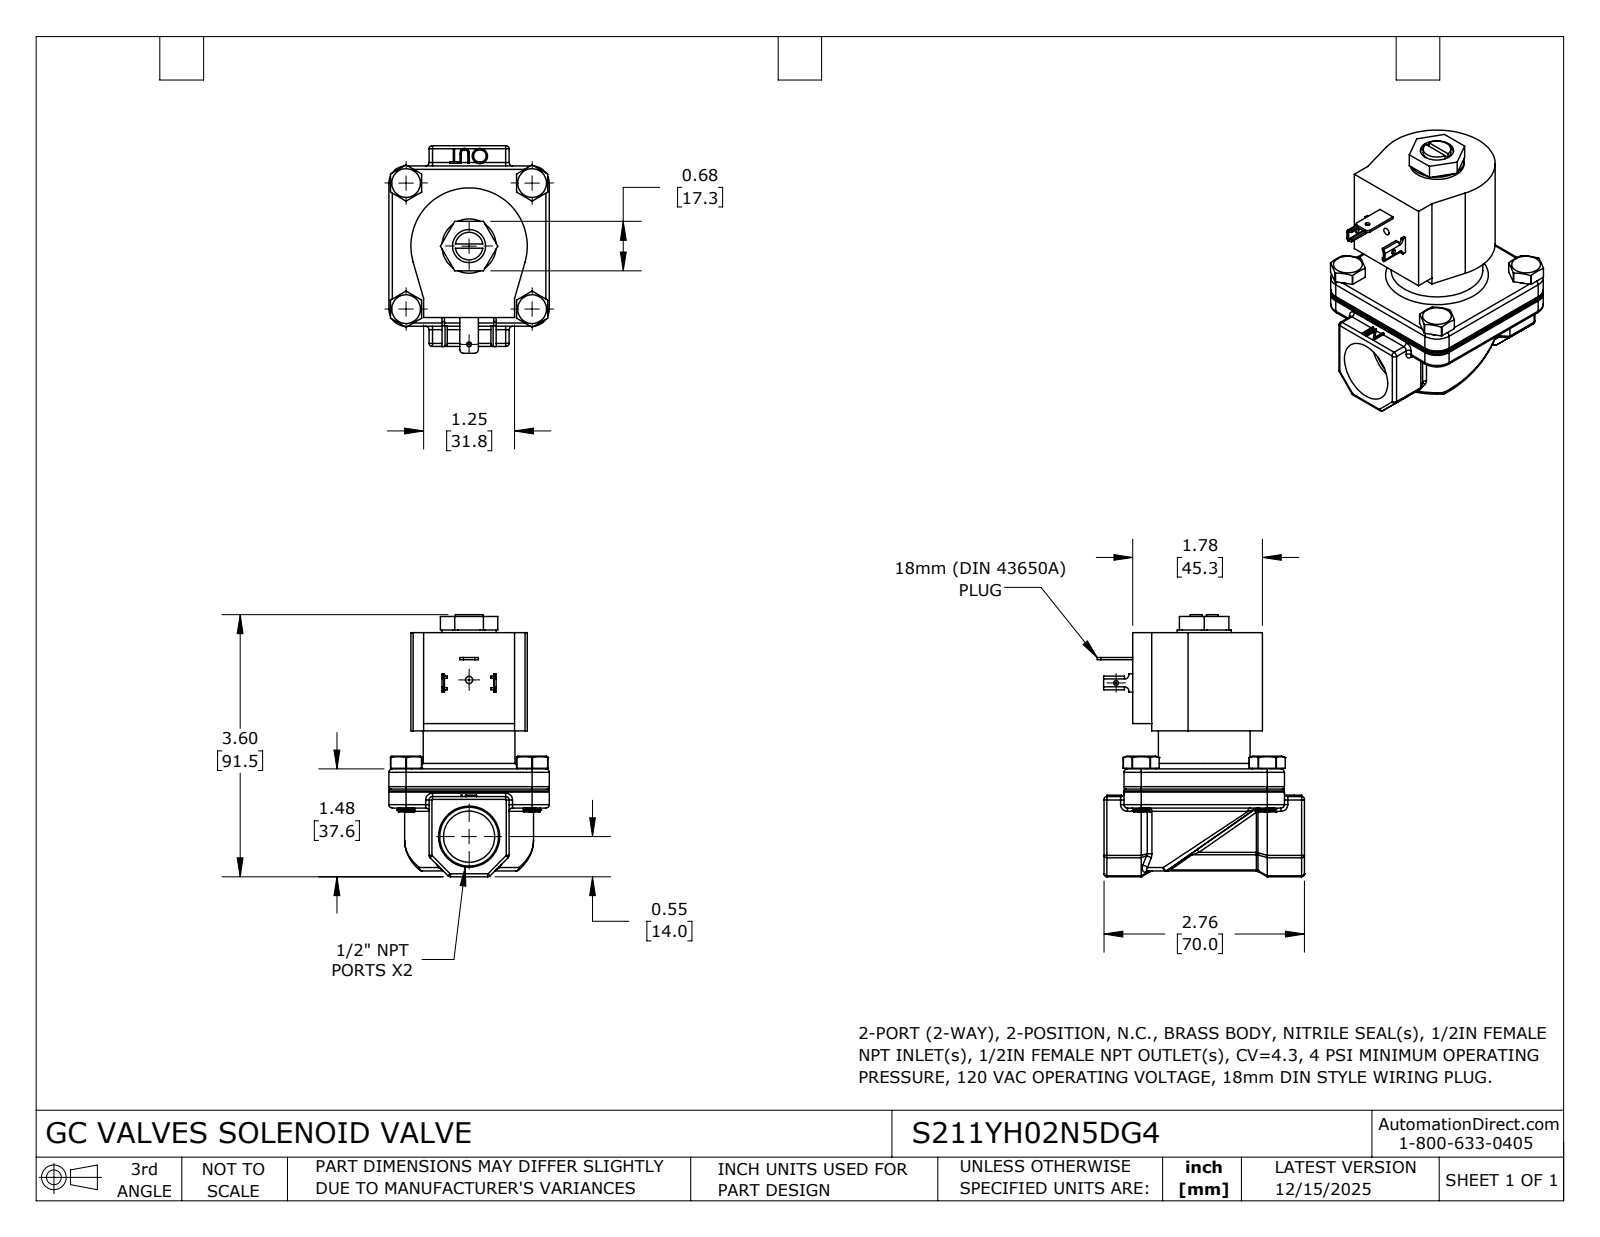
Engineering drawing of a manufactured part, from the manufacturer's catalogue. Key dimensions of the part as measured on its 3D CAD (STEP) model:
Part name (STEP PRODUCT): S211YH02N5DG4
STEP written by: SolidWorks 2024 (CONFIG_CONTROL_DESIGN)
Units: inches
Bodies: 1 solid, 521 faces (228 planar, 163 cylindrical, 130 other)
Overall size (bounding box): 3.601 × 2.851 × 2.205
Volume: 8.787 in³ · Surface area: 40.33 in²
Round holes (diameter × count): ⌀0.066 ×1, ⌀0.067 ×1, ⌀0.1 ×1, ⌀0.456 ×1, ⌀0.703 ×1
Round bosses / shafts (diameter × count): ⌀0.407 ×4, ⌀0.242 ×4, ⌀1.26 ×1, ⌀0.746 ×1, ⌀0.38 ×1
Partial cylindrical surfaces — rounded edges, fillets, slot ends (radius × count): R0.047 ×57, R0.04 ×12, R0.006 ×4, R0.031 ×4, R0.041 ×4, R0.234 ×4, R0.236 ×4, R0.05 ×2
Main face-to-face distances: 1.873, 0.551, 1.654, 0.537, 2.41, 2.205, 0.276, 2.48, 1.06, 0.523
Hole centre spacings: 1.35, 2.153
